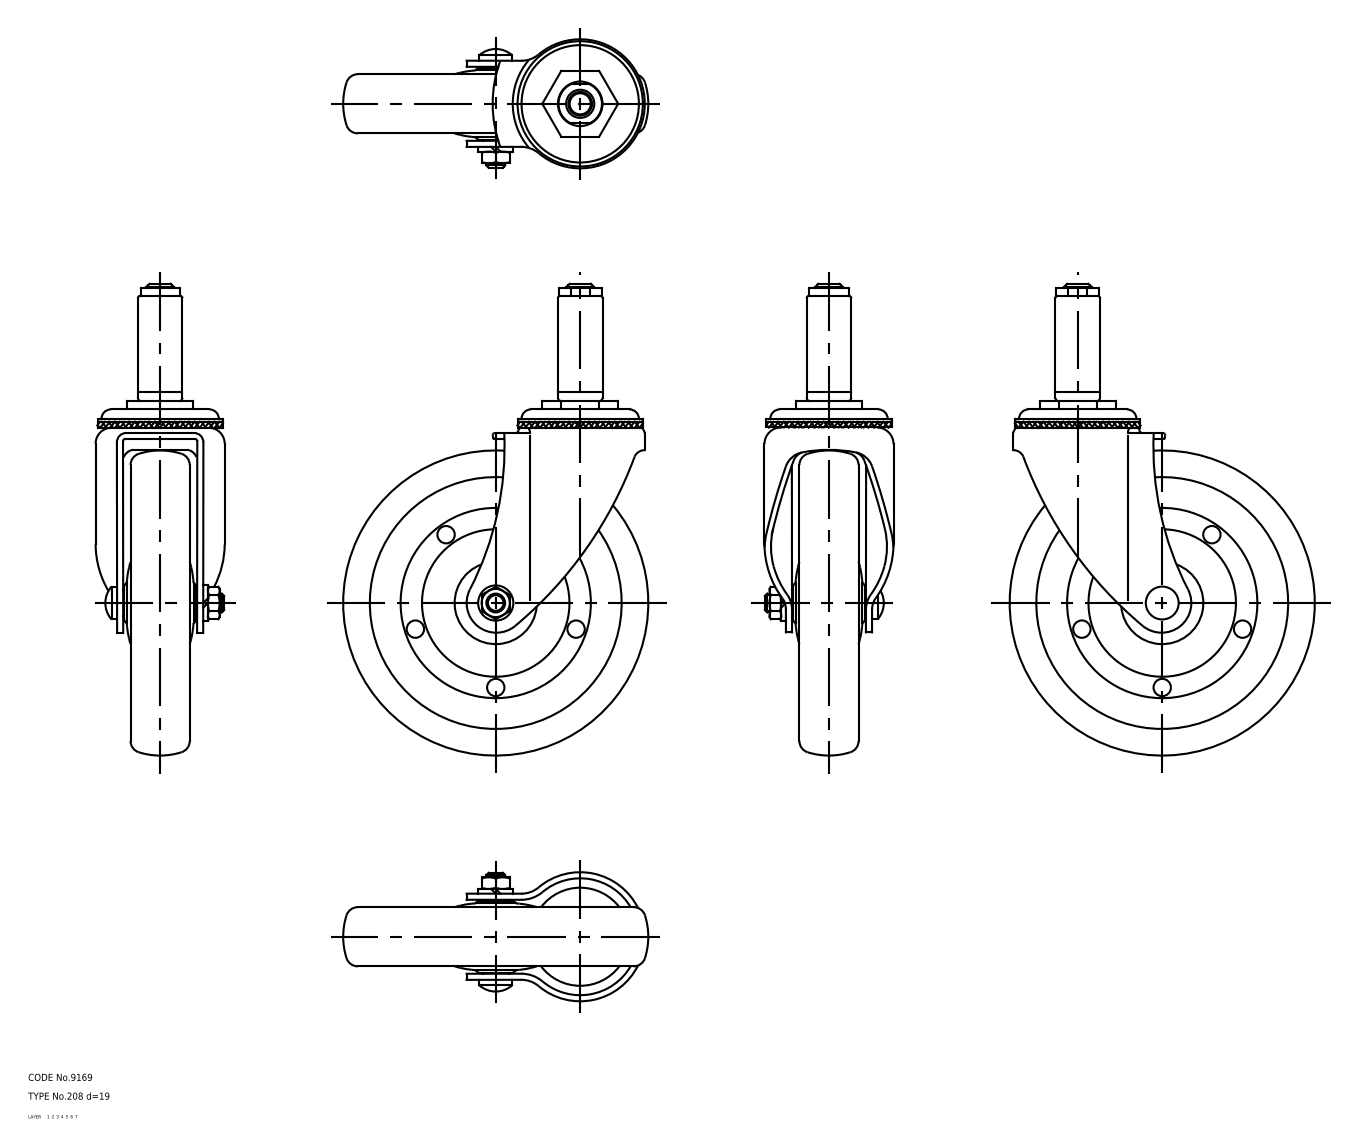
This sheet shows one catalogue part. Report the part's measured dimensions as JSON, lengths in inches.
{"part_name": "wheel; main shaft; axle; No_208_d19_22052_36", "step_written_by": "CADfix (AUTOMOTIVE_DESIGN)", "units": "inches", "bodies": {"solids": 4, "faces": 214, "planar": 0, "cylindrical": 0, "other": 214}, "overall_size": [7.913, 5.118, 2.165], "volume_in3": 18.78, "surface_area_in2": 109.6}
